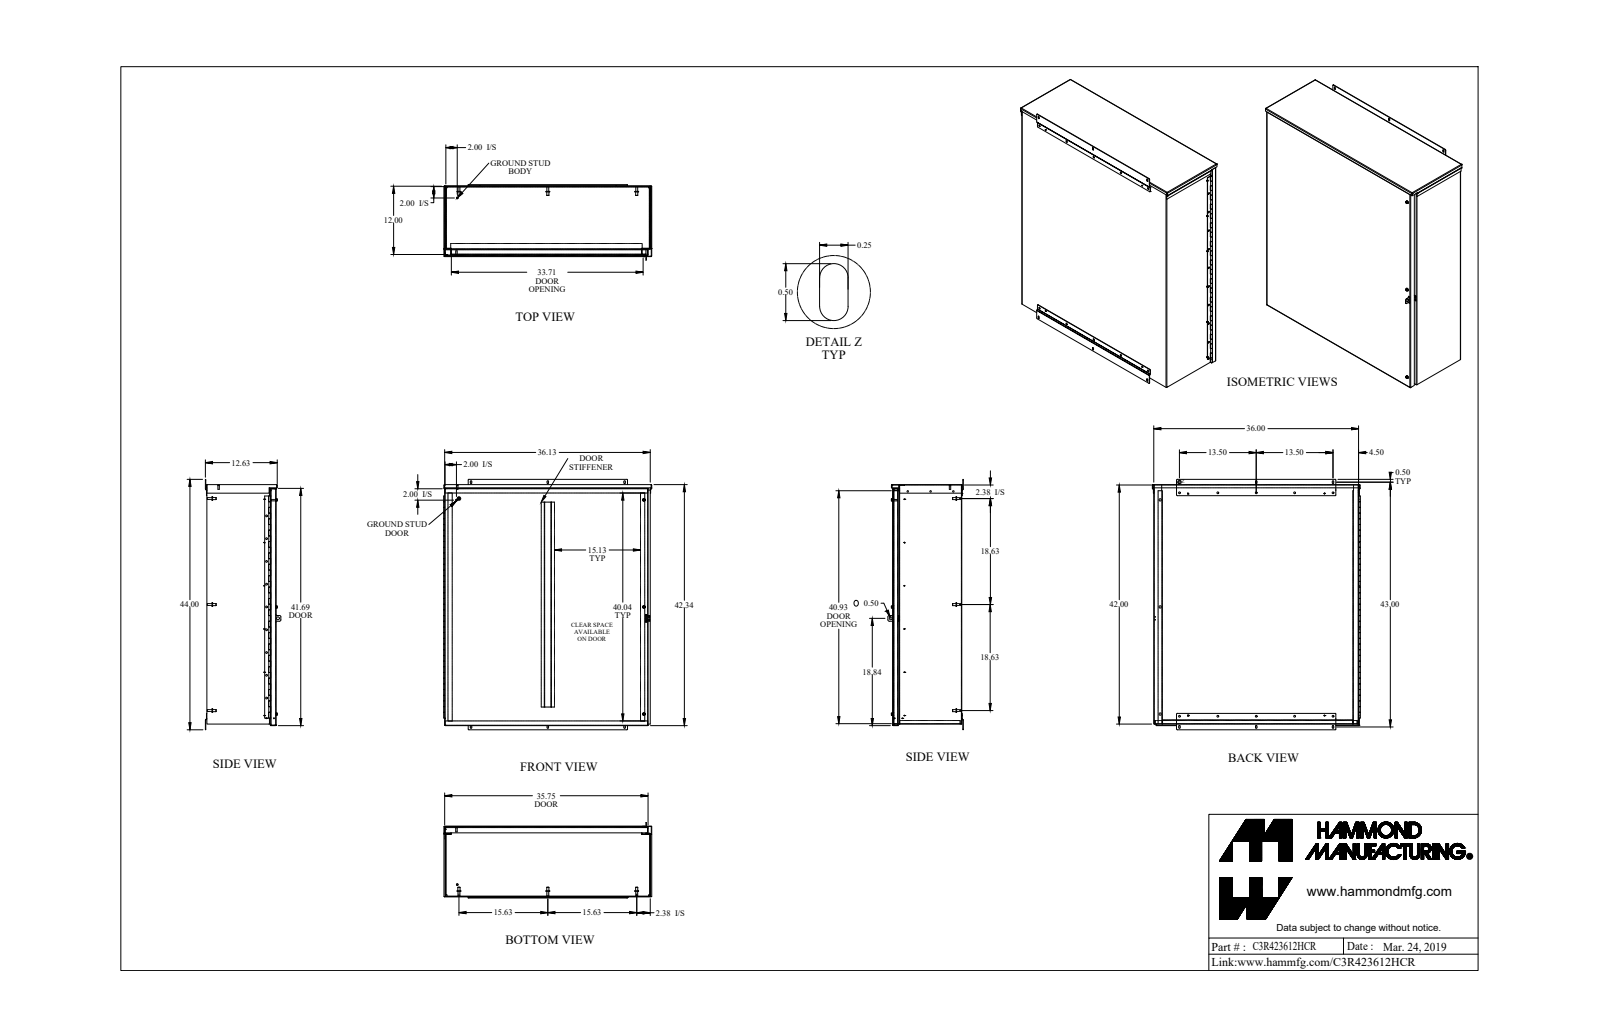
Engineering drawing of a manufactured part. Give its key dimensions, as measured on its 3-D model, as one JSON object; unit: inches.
{"part_name": "C3R423612HCR_Default", "step_written_by": "SolidWorks 2019 (CONFIG_CONTROL_DESIGN)", "units": "inches", "bodies": {"solids": 43, "faces": 1268, "planar": 653, "cylindrical": 523, "other": 92}, "overall_size": [44, 36.571, 13.26], "volume_in3": 443.2, "surface_area_in2": 12094, "round_holes": [[0.312, 10], [0.304, 9], [0.14, 4], [0.26, 4], [0.313, 4], [0.25, 3], [0.266, 3], [0.28, 3], [0.29, 3], [0.397, 3], [0.137, 2], [0.188, 1]], "round_bosses_or_shafts": [[0.131, 12], [0.65, 8], [0.375, 8], [0.33, 8], [0.51, 4], [0.244, 4], [0.187, 4], [0.5, 3]], "partial_cylinders_radius": [[0.036, 39], [0.108, 39], [0.125, 24], [0.171, 4], [0.25, 2]], "face_to_face_distances": [0.072, 12.1, 12.028, 12.172, 35.928, 42, 36, 35.856, 41.928, 42.072], "hole_center_spacings": [4, 6.75, 8, 39.826, 12, 13.5, 16, 24]}
